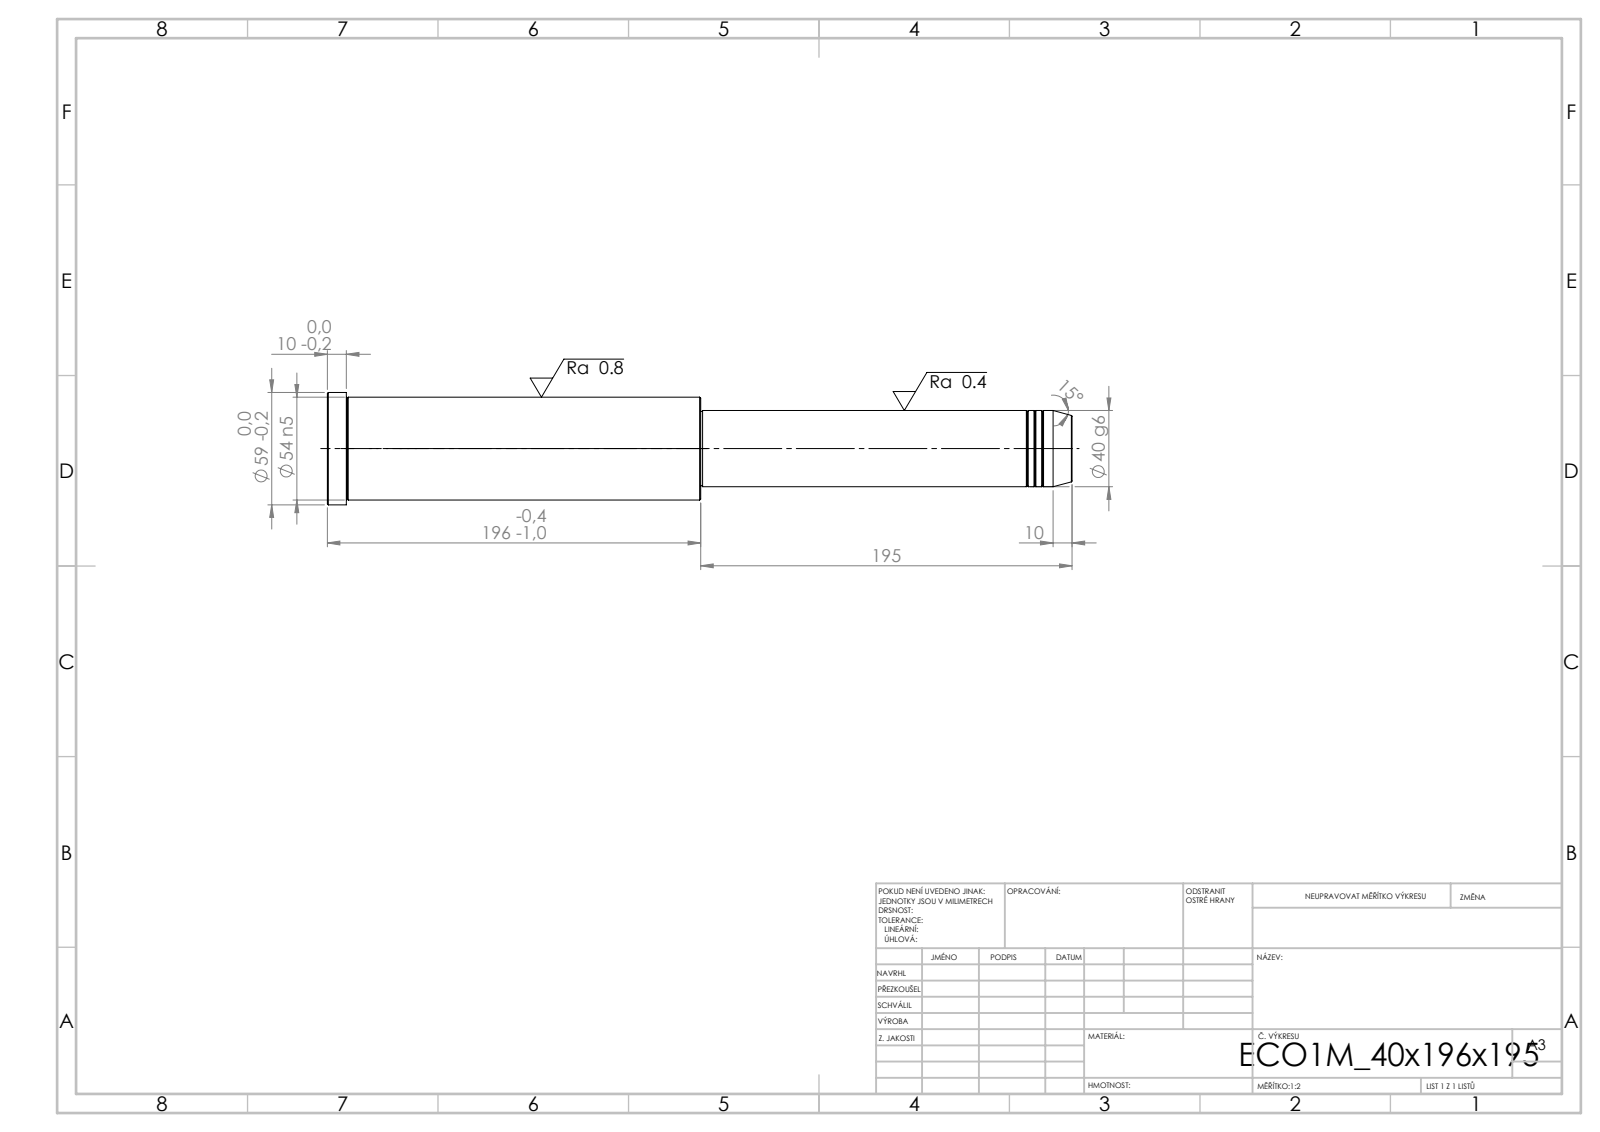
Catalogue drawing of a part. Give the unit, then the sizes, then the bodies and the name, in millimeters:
Units: millimetres
Overall size (bounding box): 391 × 59 × 59
Round bosses / shafts (diameter × count): ⌀59 ×1, ⌀54 ×1, ⌀40 ×1, ⌀39 ×1
Main face-to-face distances: 196, 195, 391, 381, 186, 10, 194, 1, 187, 197
Volume: 696 435 mm³ · Surface area: 63 327 mm²
Bodies: 1 solid, 43 faces (5 planar, 14 cylindrical, 24 other)
STEP written by: SolidWorks 2019 (CONFIG_CONTROL_DESIGN)
